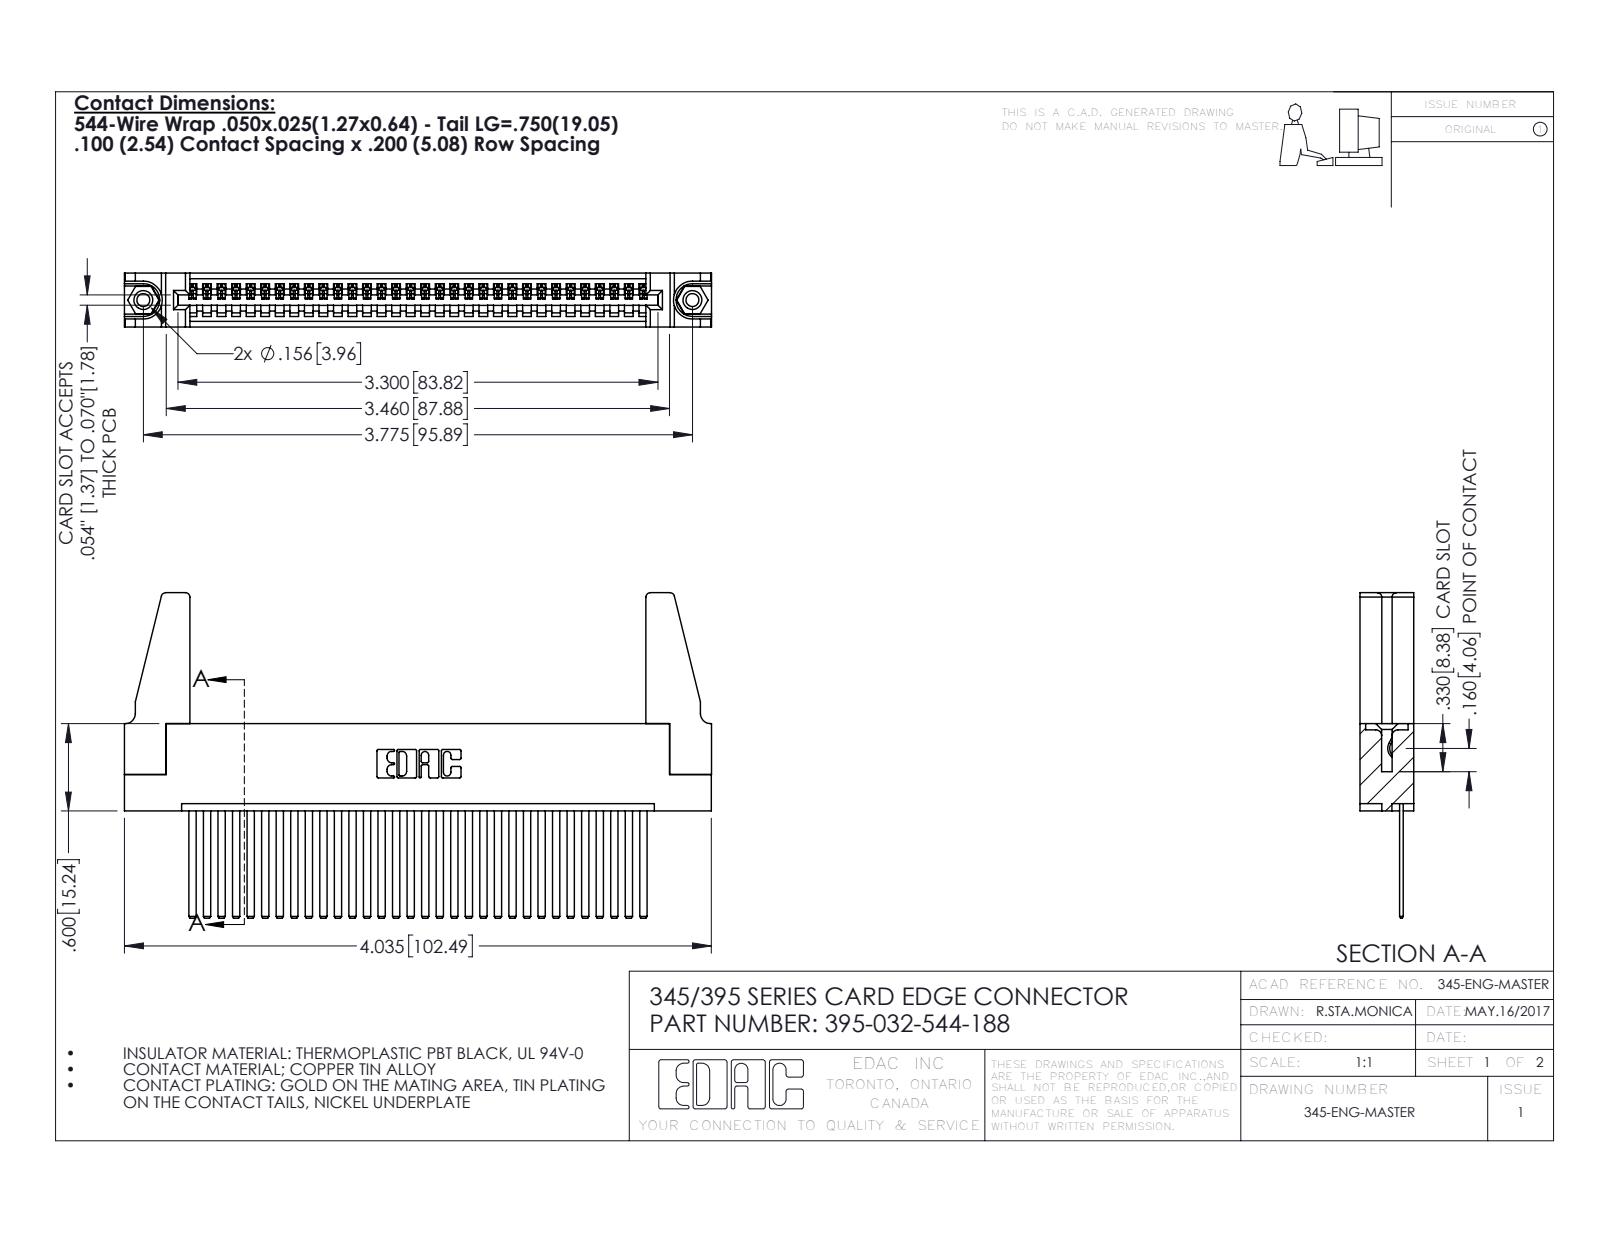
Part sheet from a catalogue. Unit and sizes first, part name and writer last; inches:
Units: inches
Overall size (bounding box): 4.036 × 2.237 × 0.37
Round holes (diameter × count): ⌀0.089 ×2, ⌀0.125 ×2, ⌀0.156 ×2, ⌀0.064 ×1
Round bosses / shafts (diameter × count): ⌀0.155 ×2
Partial cylindrical surfaces — rounded edges, fillets, slot ends (radius × count): R0.006 ×64, R0.01 ×22, R0.03 ×8, R0.007 ×6, R0.031 ×6, R0.026 ×3, R0.031 ×2, R0.04 ×2
Main face-to-face distances: 0.072, 0.298, 0.37, 0.098, 0.272, 0.025, 0.2, 0.225, 0.149, 0.072
Hole centre spacings: 0.27, 3.54, 3.775
Volume: 0.81 in³ · Surface area: 27.02 in²
Bodies: 37 solids, 1914 faces (1304 planar, 594 cylindrical, 16 other)
Part name (STEP PRODUCT): 395-032-544-188; 345 Part_Flush Mounting Lugs - 0.156 Dia-TH; 345-250-001_345-250-001-102; 345-220-078_345-220-088 (+1 more)
STEP written by: SolidWorks 2016 (CONFIG_CONTROL_DESIGN)
